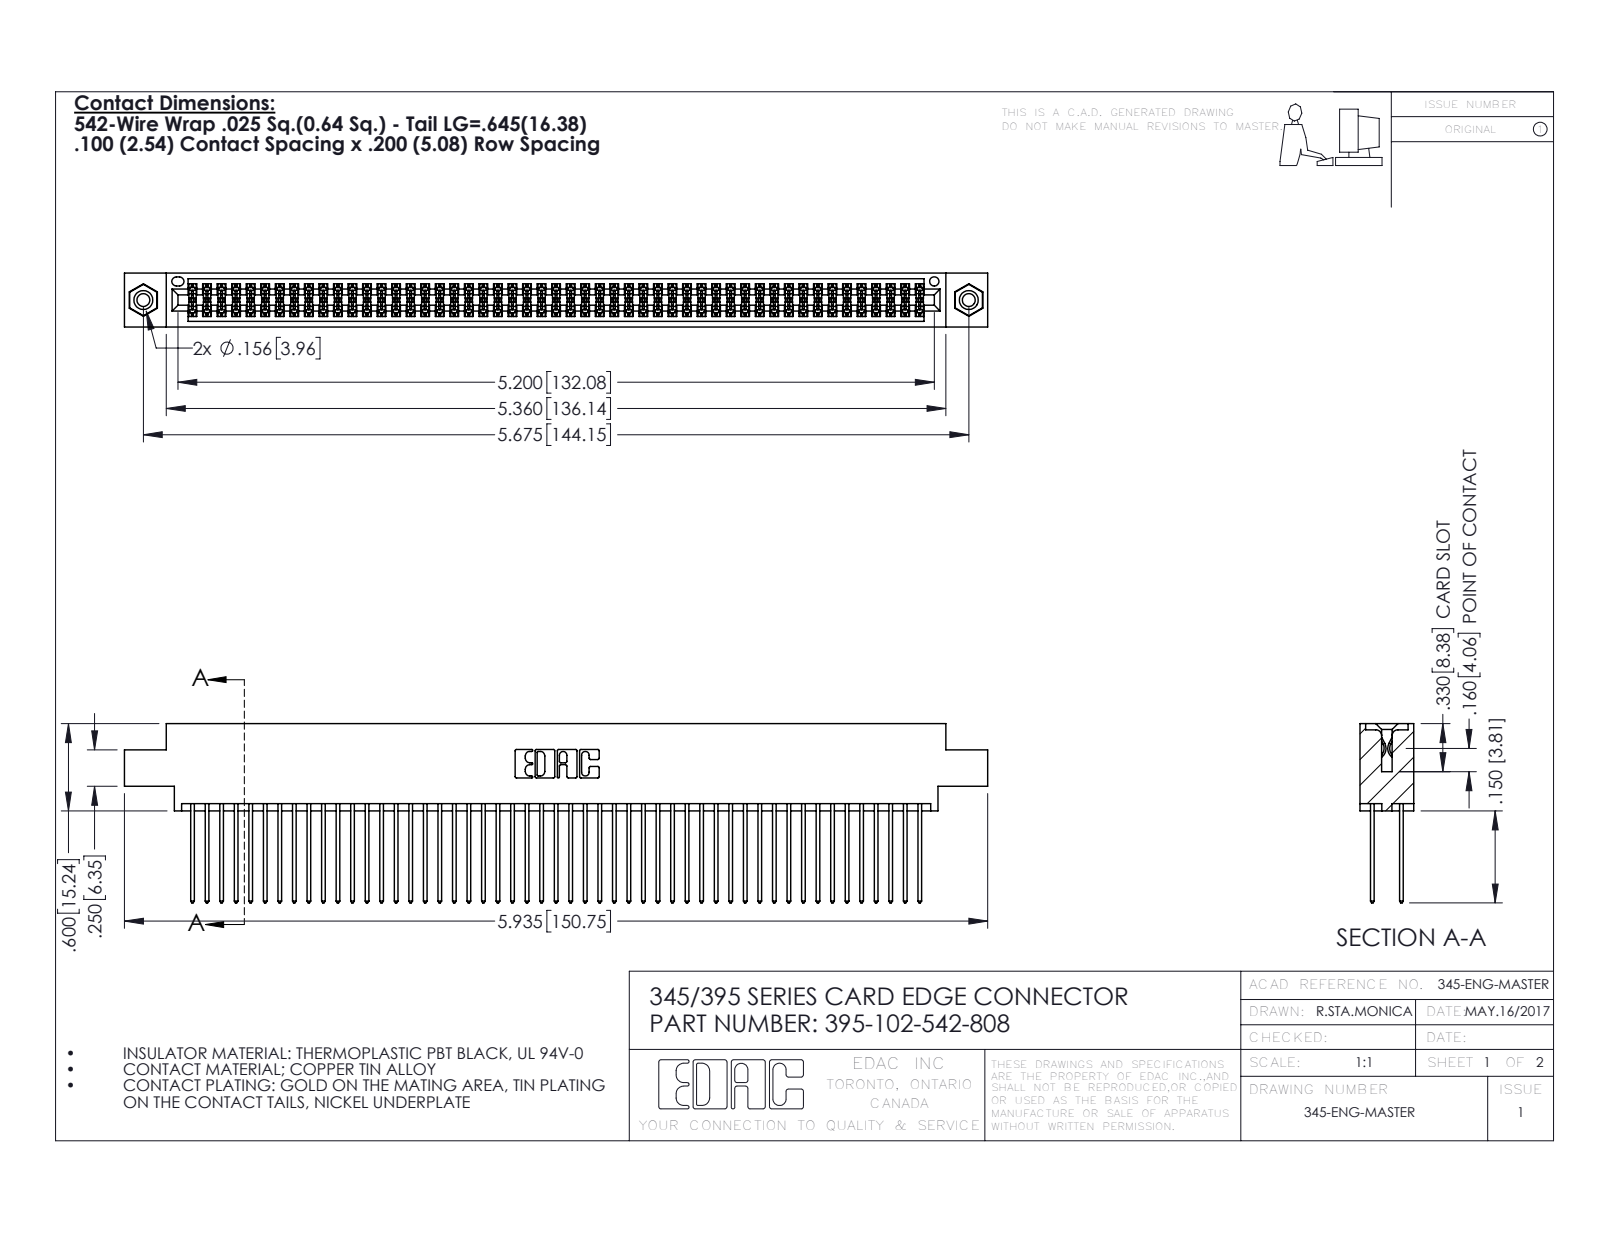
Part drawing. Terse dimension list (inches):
name: 345 Part_0.170 Offset - 0.156 Dia-TI; 395-102-542-808; 345-292-001_345-293-142; 345-250-001_345-250-003-102
written by: SolidWorks 2016 (CONFIG_CONTROL_DESIGN)
unit: in
bodies: 105 solids, 5290 faces (3482 planar, 1792 cylindrical, 16 other)
size: 5.935 × 1.232 × 0.37
volume: 0.92 in³; area: 38.52 in²
holes: 2× ⌀0.089, 2× ⌀0.125, 2× ⌀0.156, 1× ⌀0.064
bosses: 2× ⌀0.155
rounds: 153× R0.006, 102× R0.01, 22× R0.01, 6× R0.007, 6× R0.031, 3× R0.026, 2× R0.014, 2× R0.019
face distances: 0.072, 0.298, 0.2, 0.098, 0.272, 0.025, 0.37, 0.225, 0.175, 0.149
hole spacings: 0.27, 5.439, 5.675
